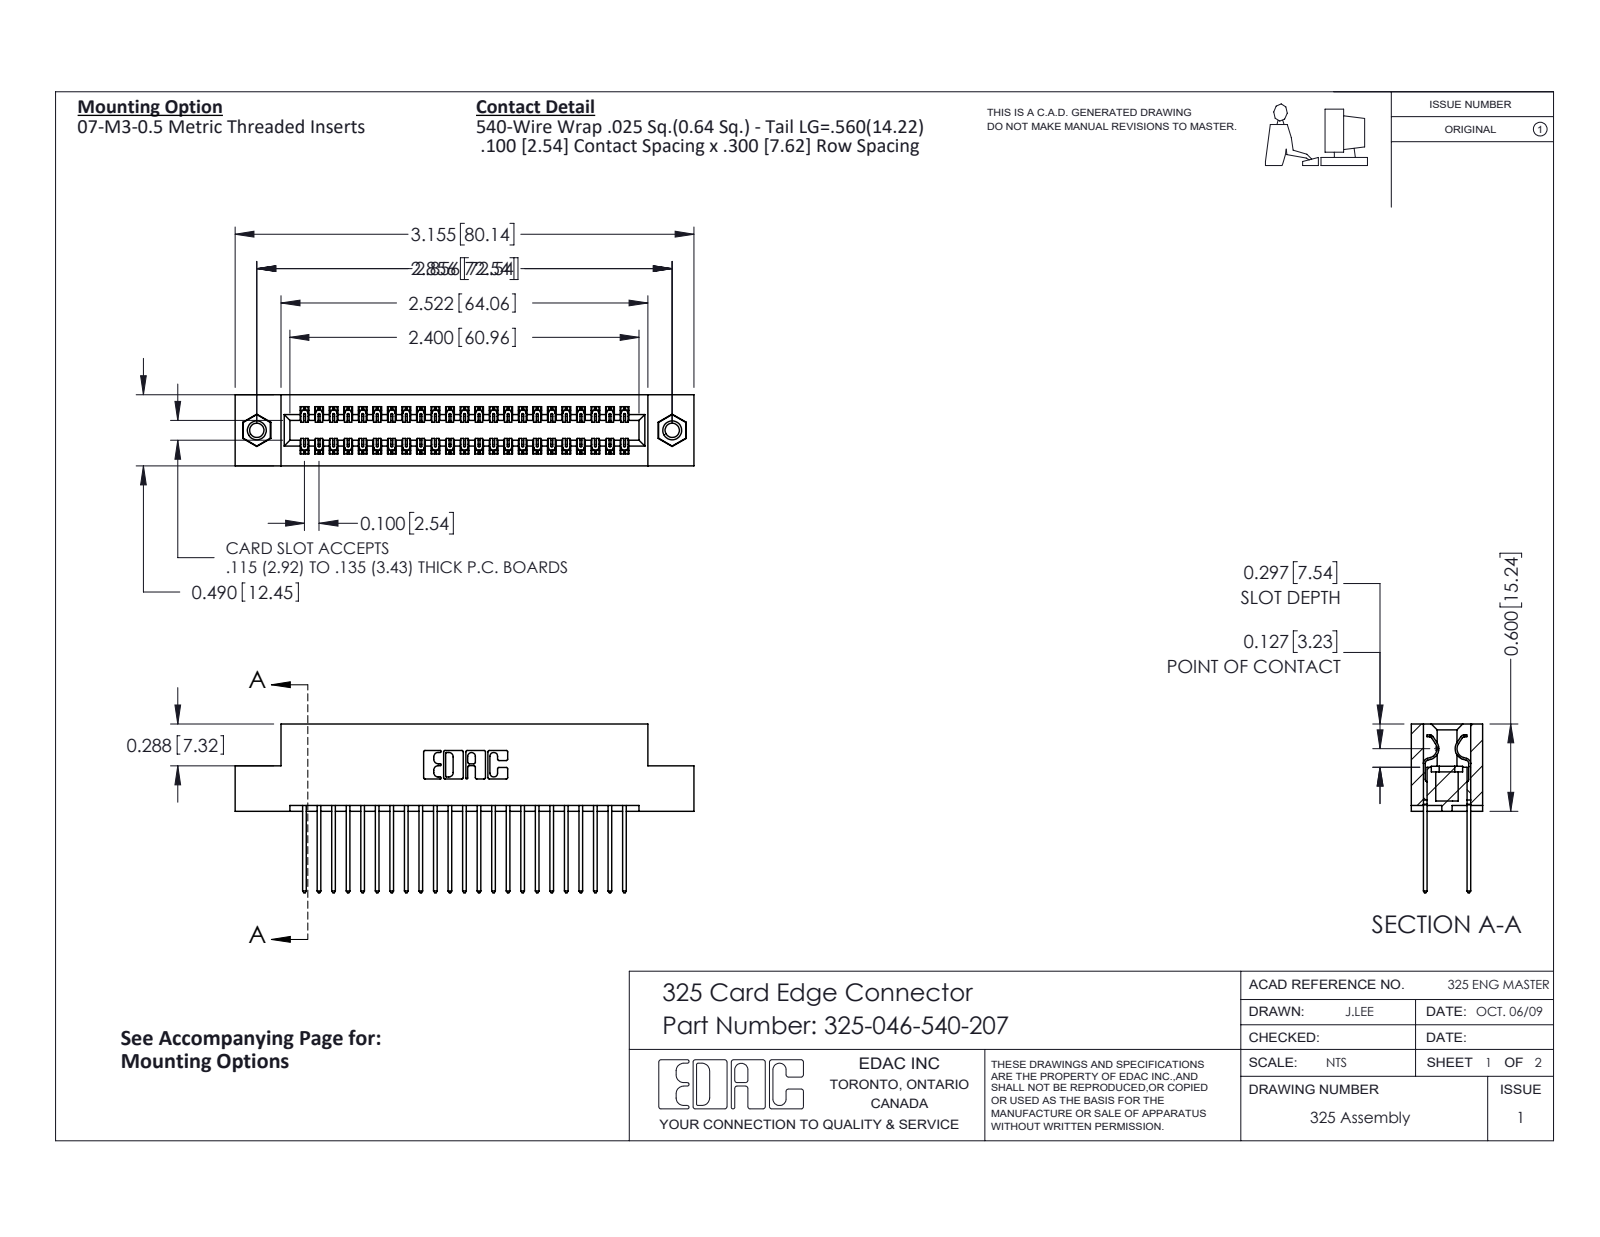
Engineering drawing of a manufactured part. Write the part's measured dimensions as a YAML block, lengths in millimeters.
part_name: "345-250-001_345-250-005-103; 325 Part_TI; 325-046-540-207; 325-292-001_325-293-140"
step_written_by: "SolidWorks 2016 (CONFIG_CONTROL_DESIGN)"
units: millimeters
bodies: {solids: 49, faces: 2566, planar: 1758, cylindrical: 792, other: 16}
overall_size: [80.1, 29.5, 12.4]
volume: 10300
surface_area: 12920
round_holes:
  - {diameter: 2.5, count: 2}
  - {diameter: 3.2, count: 2}
  - {diameter: 4.1, count: 2}
round_bosses_or_shafts:
  - {diameter: 3.9, count: 2}
partial_cylinders:
  - {radius: 0.2, count: 69}
  - {radius: 0.3, count: 46}
  - {radius: 0.3, count: 22}
  - {radius: 0.2, count: 6}
  - {radius: 0.8, count: 6}
  - {radius: 0.7, count: 3}
  - {radius: 0.4, count: 2}
  - {radius: 0.6, count: 2}
face_to_face_distances: [2.1, 10.3, 7.6, 2.7, 9.7, 0.6, 12.4, 8.3, 7, 1]
hole_center_spacings: [72.5]
